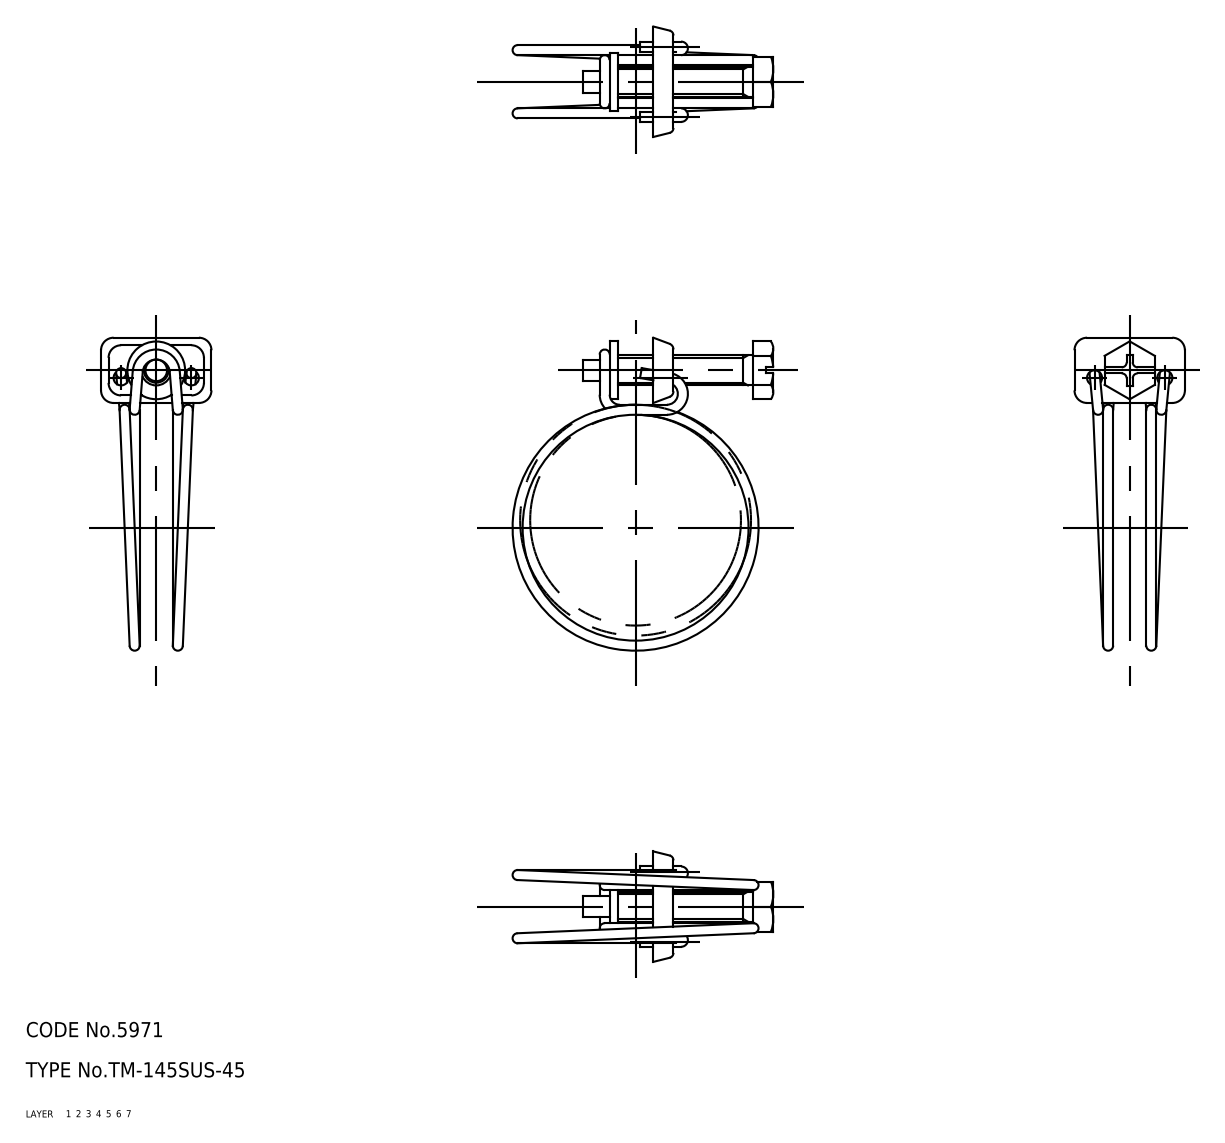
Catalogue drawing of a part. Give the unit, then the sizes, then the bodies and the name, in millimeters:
Units: millimetres
Overall size (bounding box): 62.35 × 51.95 × 22
Volume: 2 997 mm³ · Surface area: 4 307 mm²
Bodies: 3 solids, 119 faces (0 planar, 0 cylindrical, 119 other)
Part name (STEP PRODUCT): screw; holder; band; TM_145SUS_45_22209_36
STEP written by: CADfix (AUTOMOTIVE_DESIGN)
